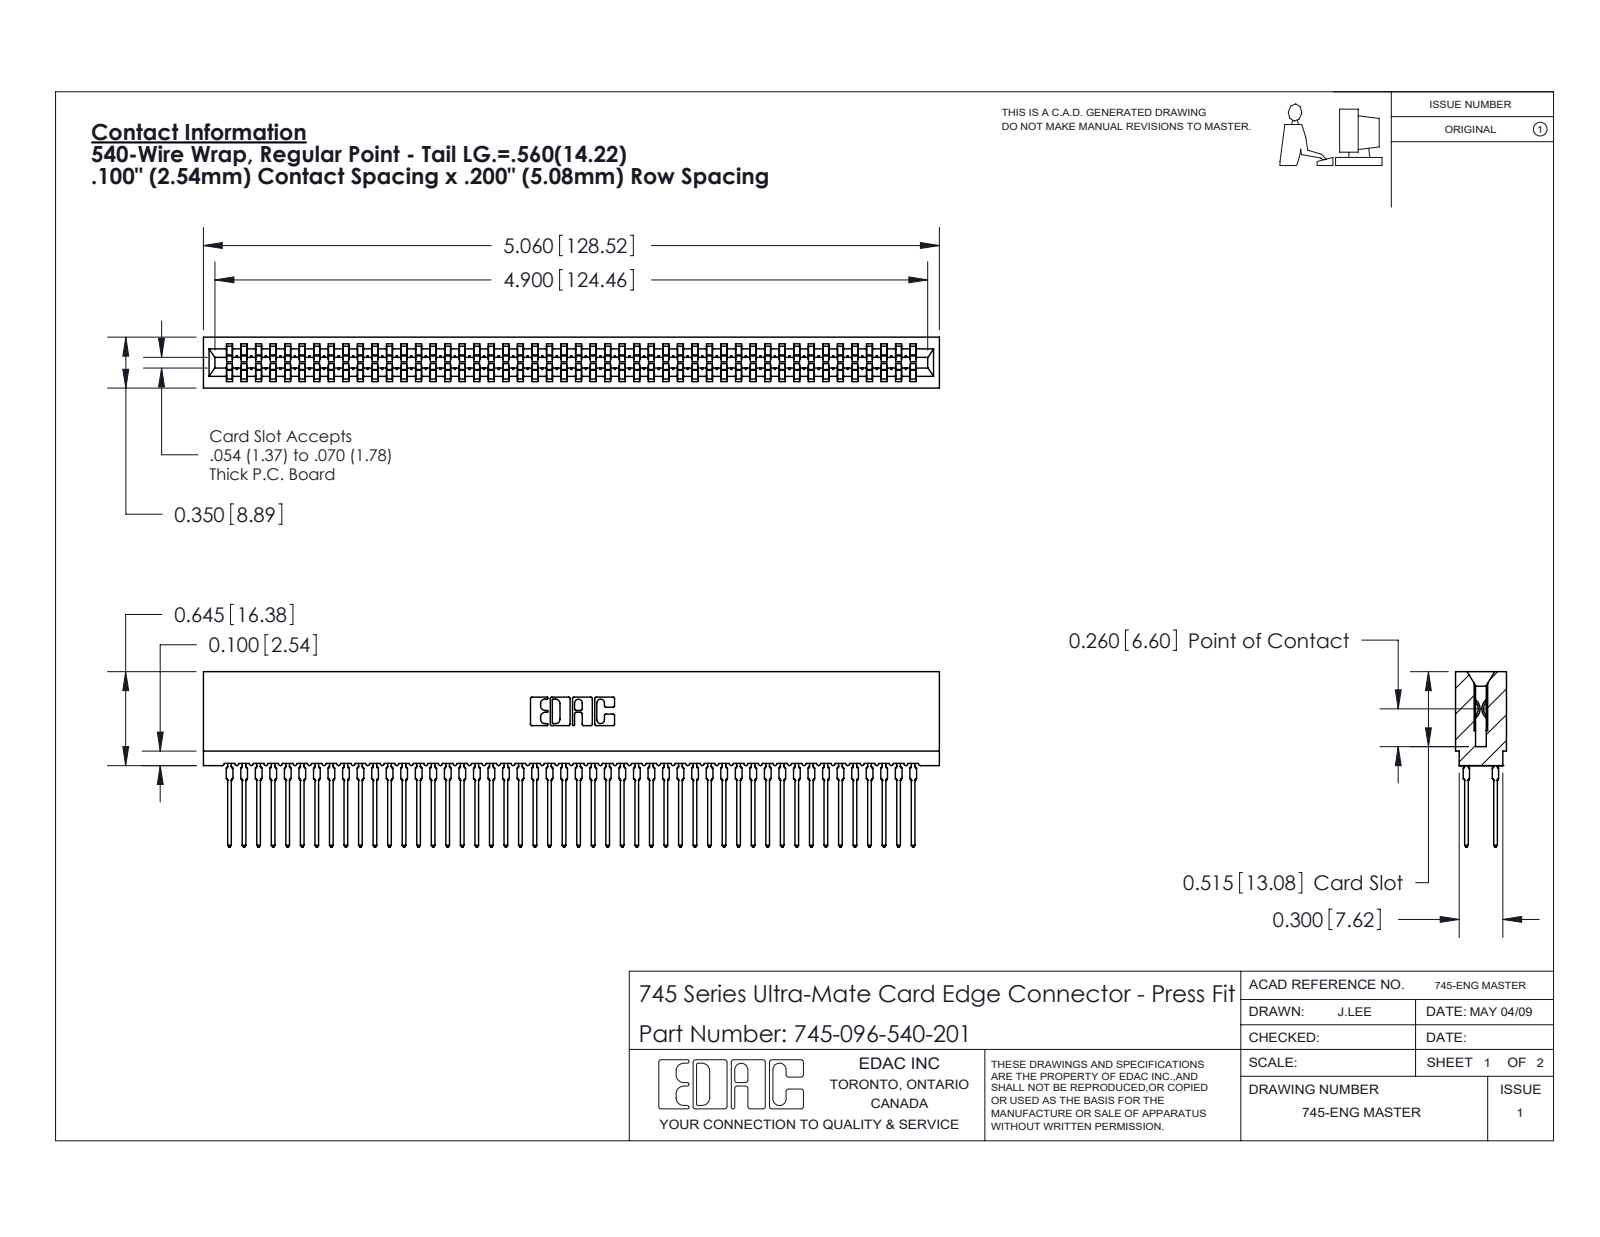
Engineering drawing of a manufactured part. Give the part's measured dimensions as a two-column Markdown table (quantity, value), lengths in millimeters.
| quantity | value |
| --- | --- |
| part name | 745-292-001_540; 745-096-540-201; 745 Part_Insulator Option - 01 |
| STEP written by | SolidWorks 2020 (CONFIG_CONTROL_DESIGN) |
| units | millimeters |
| bodies | 97 solids, 8687 faces (4471 planar, 1720 cylindrical, 2496 other) |
| overall size | 128.5 × 30.6 × 8.9 |
| volume | 11 800 mm³ |
| surface area | 25 280 mm² |
| partial cylindrical surfaces (radius × count) | 0.5 × 192, 0.4 × 96, 0.3 × 22, 0.1 × 8, 0.3 × 8, 0.2 × 6, 0.8 × 6, 0.7 × 3 |
| main face-to-face distances | 1.6, 7.3, 8.9, 5.1, 1.1, 7.7, 0.5, 6.2, 3.5, 5.4 |
